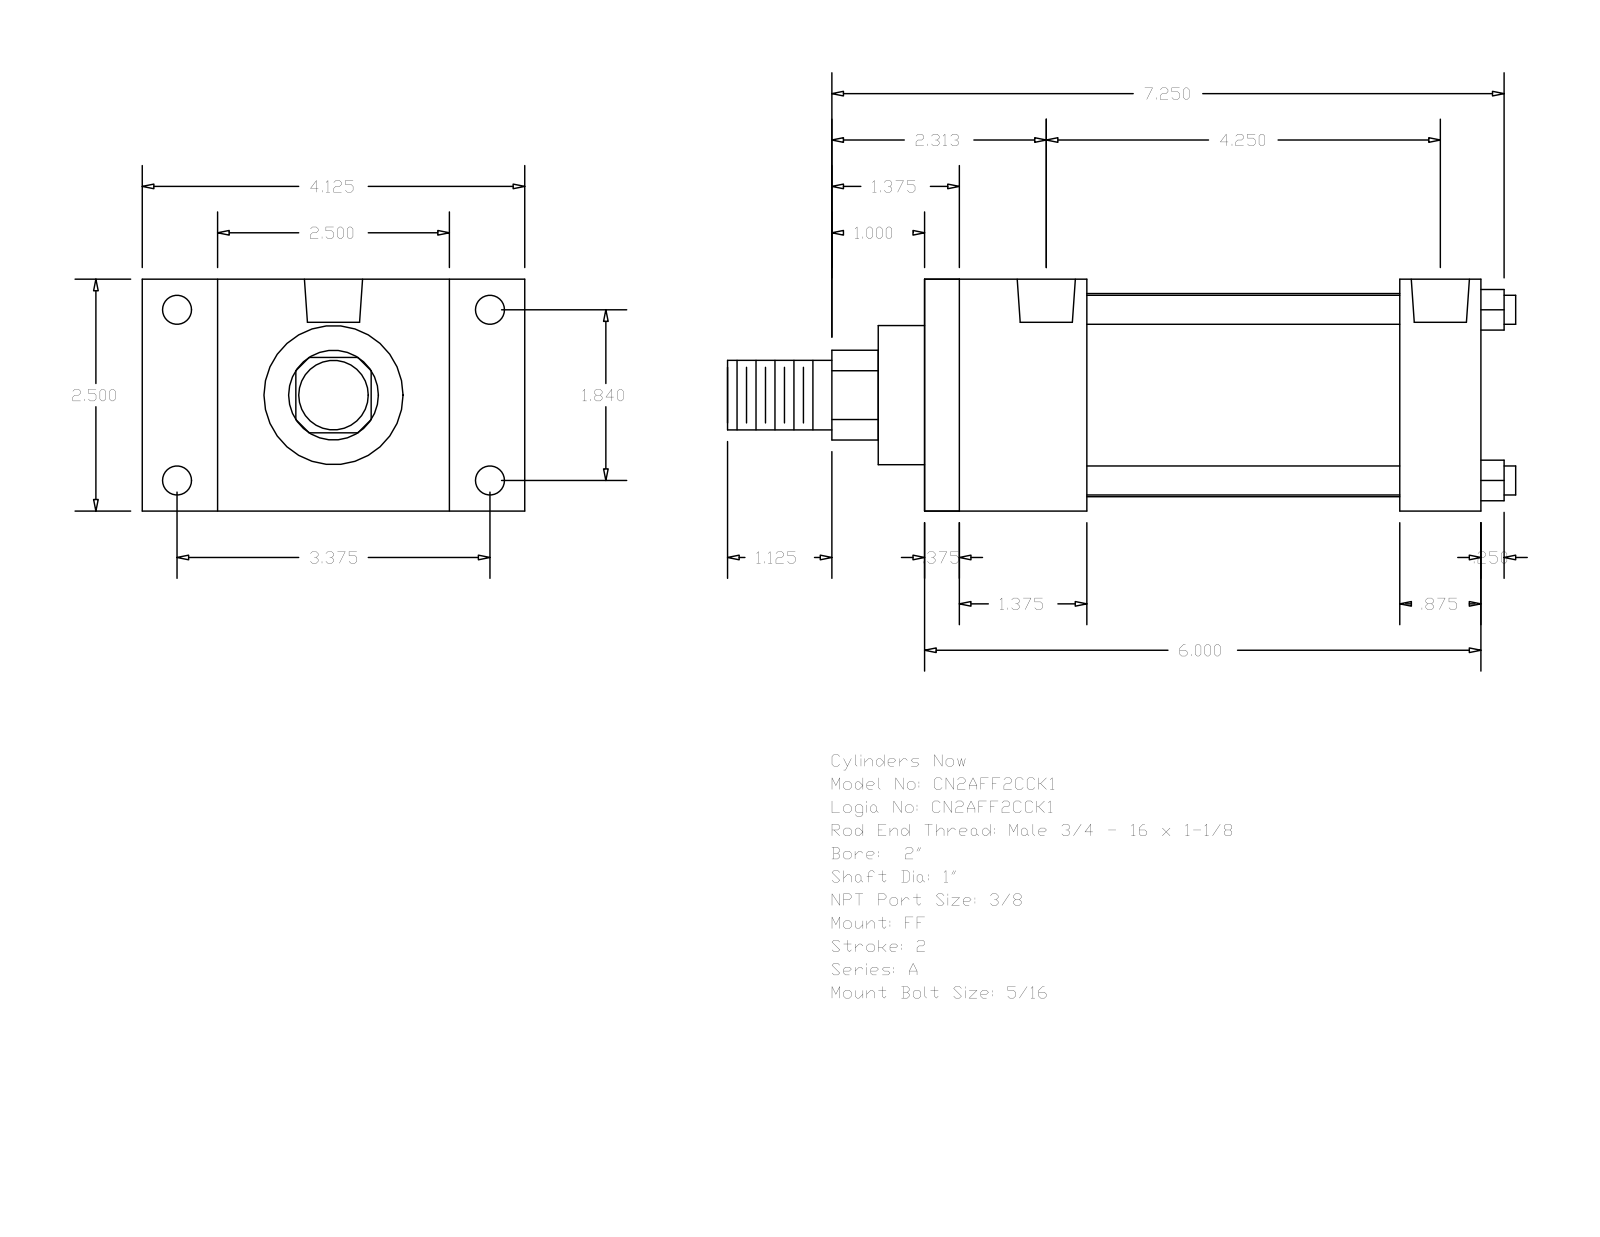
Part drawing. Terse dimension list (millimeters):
name: A_FF__0200_1
written by: GSSL Pune (CONFIG_CONTROL_DESIGN)
unit: mm
bodies: 0 solids, 92 faces (64 planar, 28 cylindrical, 0 other)
size: 215.9 × 104.78 × 63.5
holes: 4× ⌀5.56, 4× ⌀7.94, 2× ⌀15.93
bosses: 4× ⌀7.94, 1× ⌀55.63, 1× ⌀38.1, 1× ⌀25.4, 1× ⌀19.05
rounds: 1× R12.29
face distances: 63.5, 152.4, 9.52, 142.88, 20.64, 44.45, 130.17, 34.93, 120.65, 85.72
hole spacings: 46.74, 85.72, 97.63, 102.38, 1.59, 3.98, 103.97, 106.36
